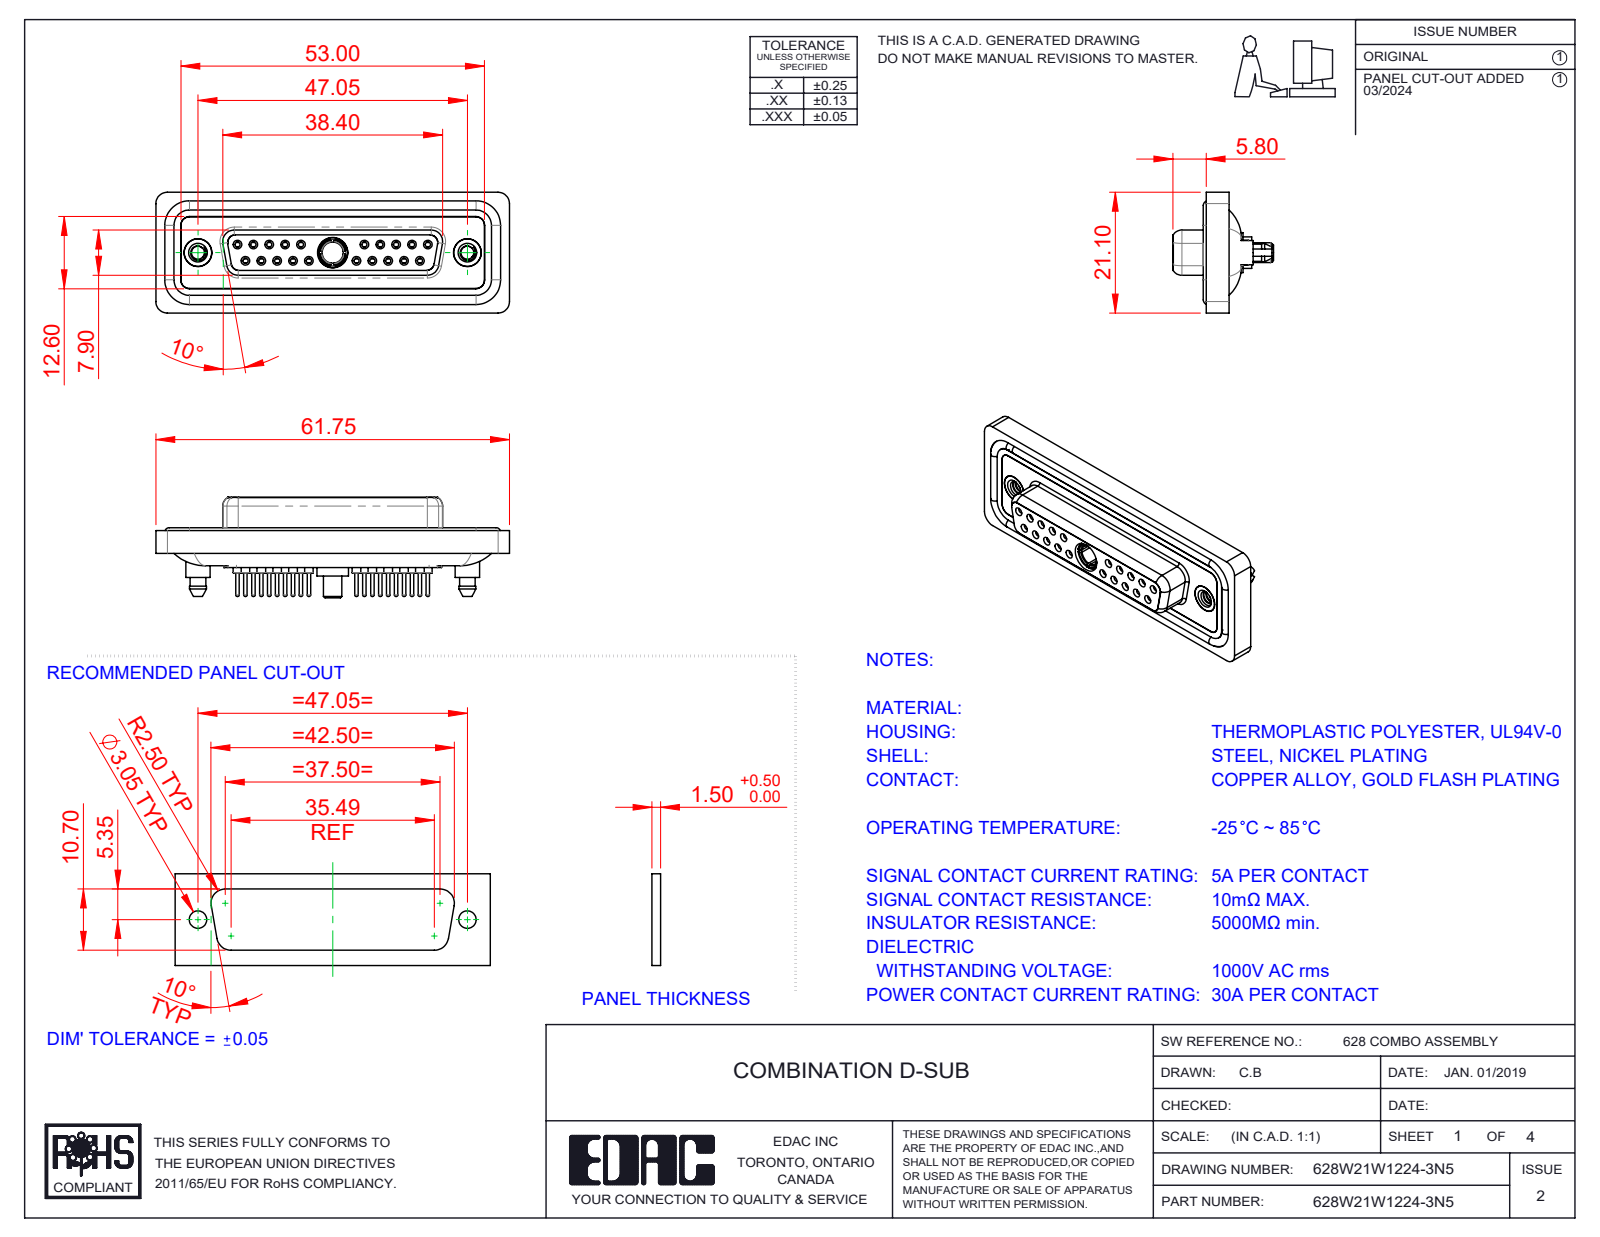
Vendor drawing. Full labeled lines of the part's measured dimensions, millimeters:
Part name (STEP PRODUCT): 628Combo Shell Rear_25 Contacts; 628Combo Waterproof Housing_25 Contacts; 628Combo Contact Row 1_24; 628W21W1224-3N5 (+5 more)
STEP written by: SolidWorks 2023 (CONFIG_CONTROL_DESIGN)
Units: millimetres
Bodies: 29 solids, 1610 faces (450 planar, 623 cylindrical, 537 other)
Overall size (bounding box): 61.75 × 21.1 × 17.55
Volume: 8 515 mm³ · Surface area: 14 340 mm²
Round holes (diameter × count): ⌀0.9 ×20, ⌀1.1 ×20, ⌀1.5 ×20, ⌀2 ×20, ⌀1.6 ×10, ⌀1.7 ×10, ⌀4.85 ×3, ⌀2.26 ×2, ⌀4 ×2, ⌀4.05 ×2, ⌀5 ×2, ⌀3.7 ×1
Round bosses / shafts (diameter × count): ⌀2.2 ×20, ⌀0.6 ×20, ⌀1.6 ×14, ⌀5.4 ×2, ⌀4.95 ×2, ⌀4.8 ×2, ⌀4.25 ×2, ⌀5.5 ×1
Partial cylindrical surfaces — rounded edges, fillets, slot ends (radius × count): R1.5 ×24, R2 ×18, R1.6 ×10, R1.35 ×8, R0.25 ×4, R0.5 ×4, R0.6 ×4, R0.65 ×4
Main face-to-face distances: 0.4, 1.8, 7.45, 6.6, 5.65, 1.6, 0.5, 7.05, 2.9, 1.1
Hole centre spacings: 3.16, 2.77, 5.54, 5.03, 8.31, 7.48, 16.62, 19.39
